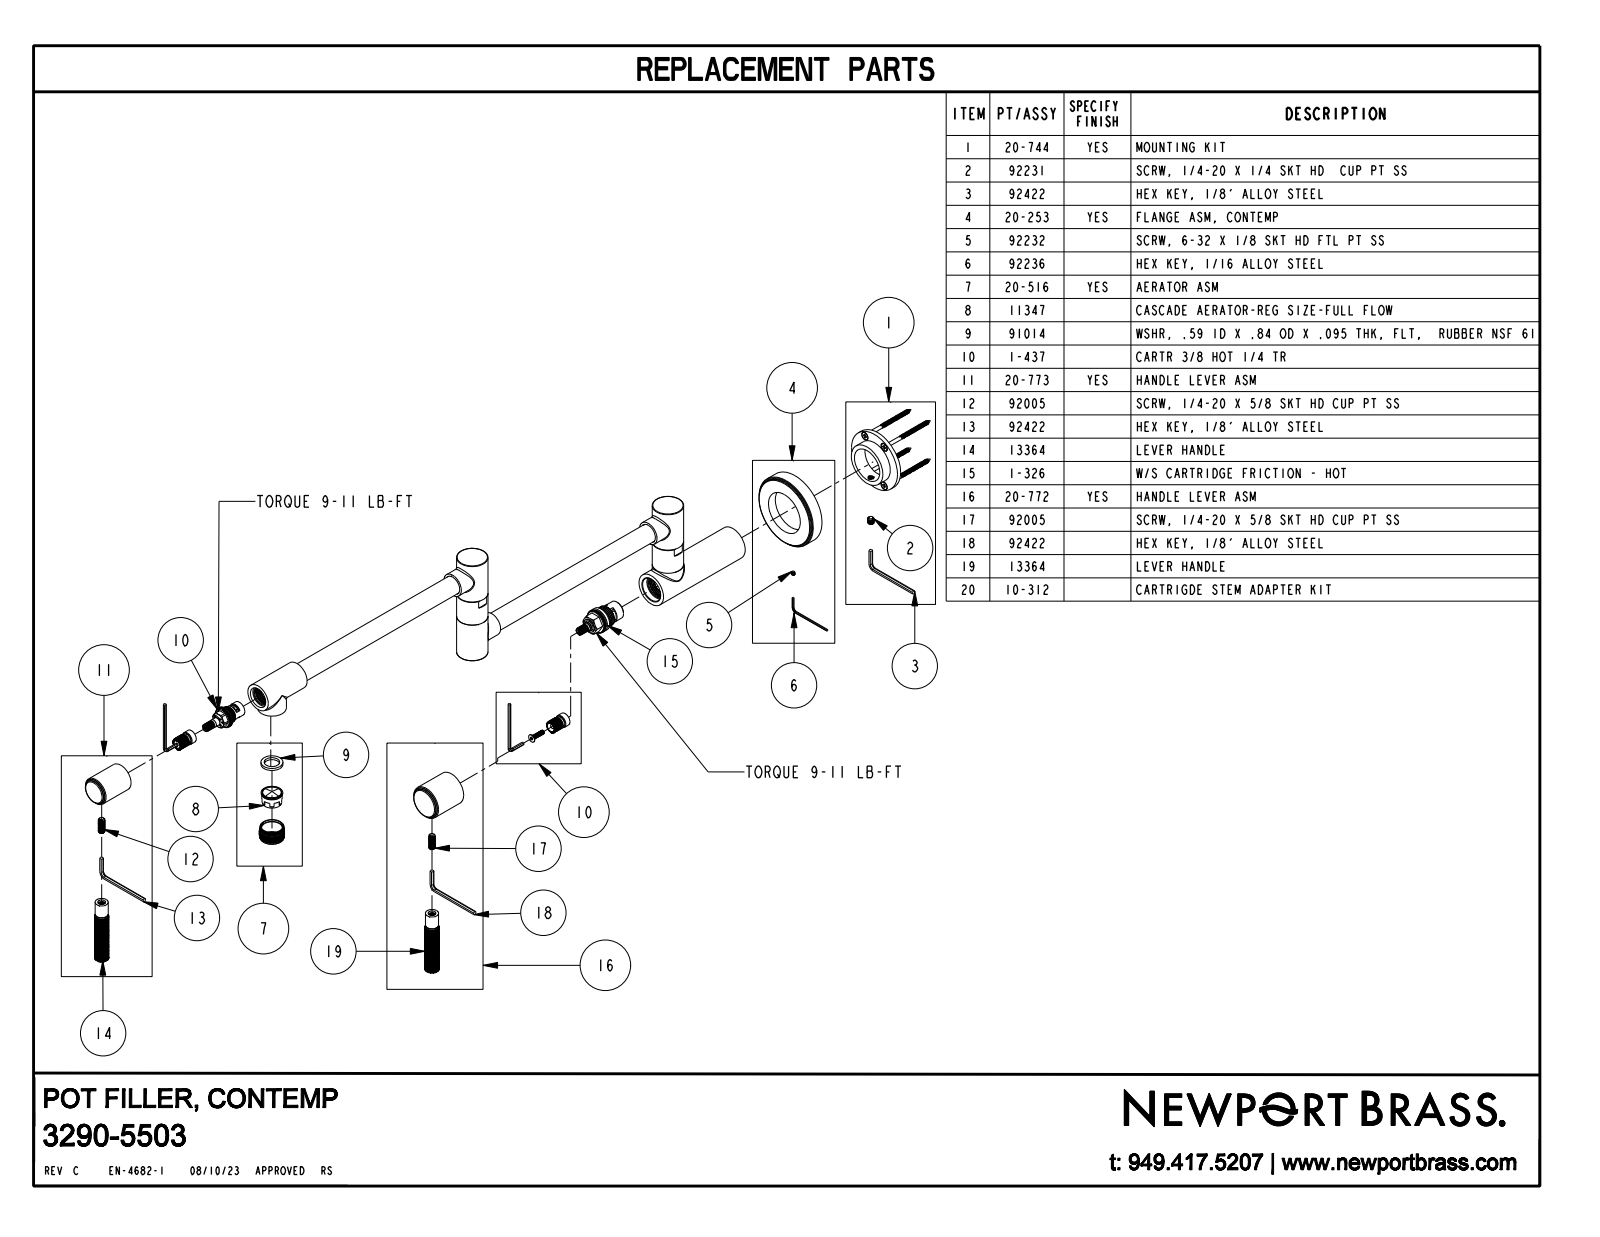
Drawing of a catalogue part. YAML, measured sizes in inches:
part_name: "3290-5503"
step_written_by: "CREO PARAMETRIC BY PTC INC, 2018400 (CONFIG_CONTROL_DESIGN)"
units: inches
bodies: {solids: 1, faces: 12378, planar: 35, cylindrical: 2431, other: 9912}
overall_size: [27.126, 9.441, 2.92]
volume: 32.92
surface_area: 146.5
round_bosses_or_shafts:
  - {diameter: 0.94, count: 4}
  - {diameter: 1.2, count: 2}
  - {diameter: 1.1, count: 2}
  - {diameter: 0.75, count: 2}
  - {diameter: 0.54, count: 2}
  - {diameter: 0.5, count: 2}
  - {diameter: 2.92, count: 1}
  - {diameter: 2.77, count: 1}
partial_cylinders:
  - {radius: 0.472, count: 1}
face_to_face_distances: [0.57, 2.86, 0.02, 1.576, 4.437, 5.327, 5.897, 1.676, 1.696, 4.43]
